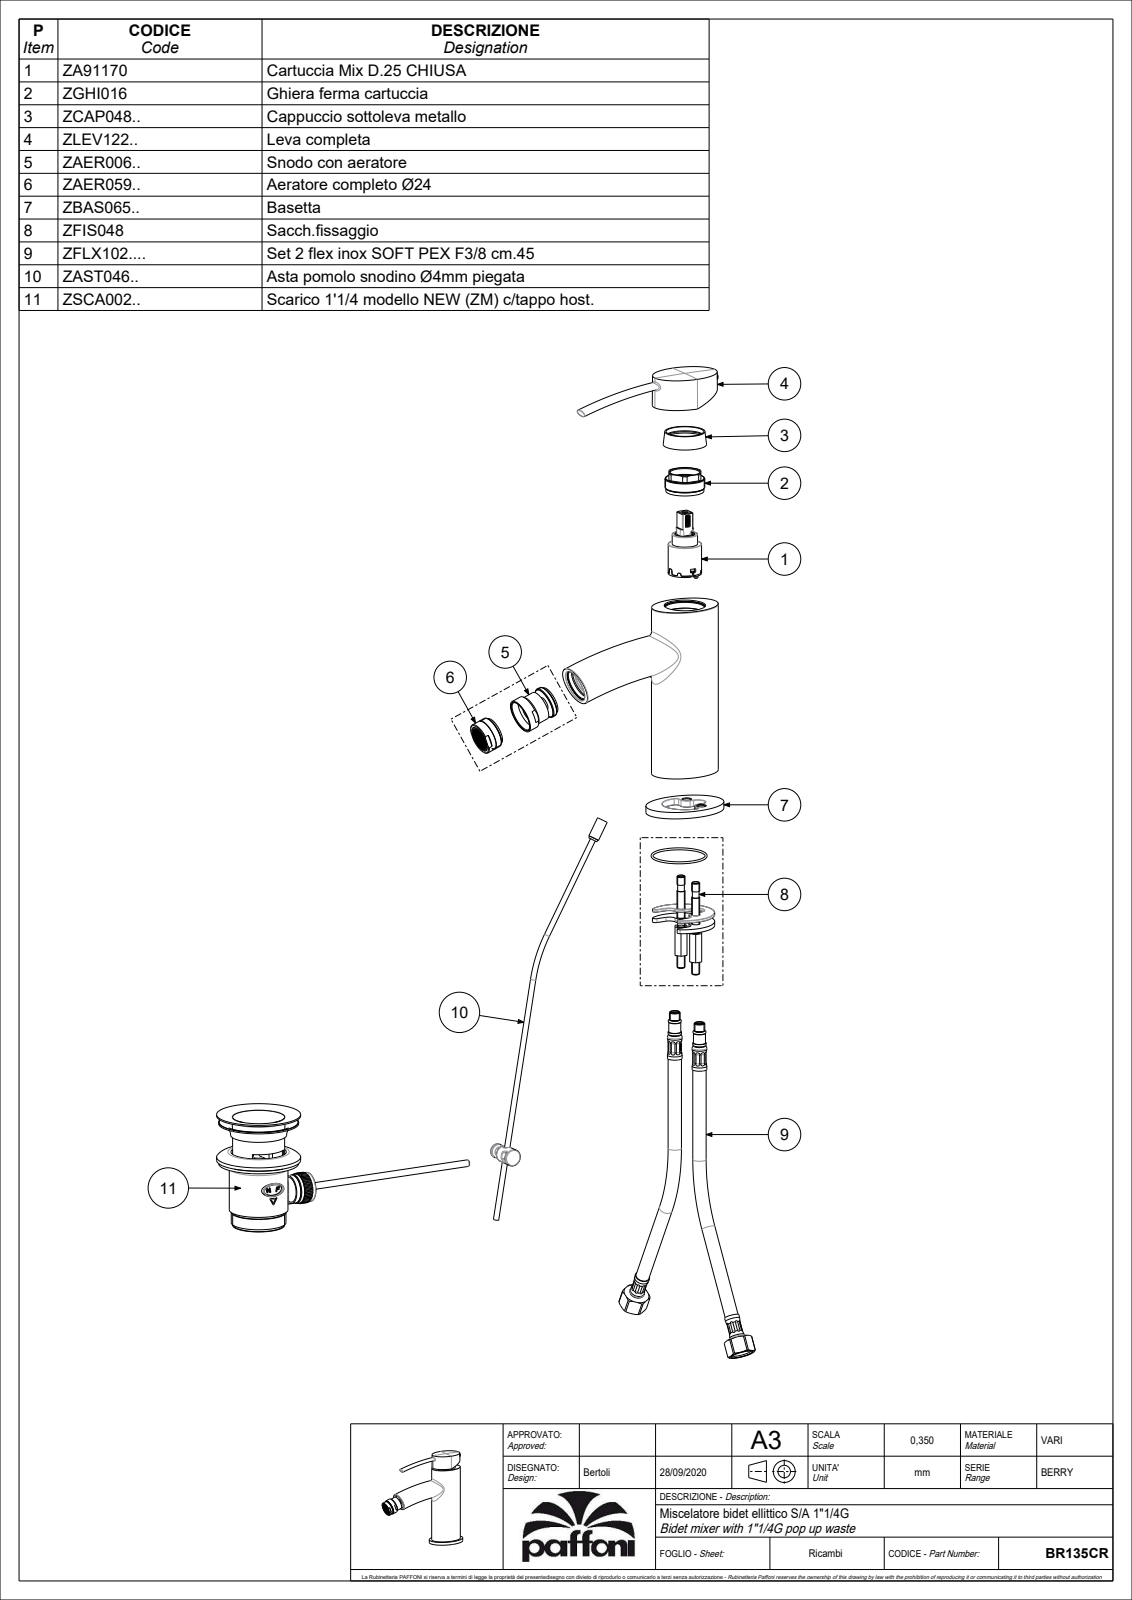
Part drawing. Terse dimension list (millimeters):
name: BR135CR
written by: CREO PARAMETRIC BY PTC INC, 2020044 (CONFIG_CONTROL_DESIGN)
unit: mm
bodies: 7 solids, 2791 faces (1989 planar, 423 cylindrical, 379 other)
size: 170.07 × 159.2 × 46
volume: 165 111 mm³; area: 99 702 mm²
holes: 3× ⌀4.5, 3× ⌀5, 3× ⌀7, 2× ⌀3, 2× ⌀5.5, 2× ⌀6.2, 2× ⌀6.5, 2× ⌀9.4, 2× ⌀16, 2× ⌀20, 1× ⌀5.3, 1× ⌀8
bosses: 3× ⌀10, 3× ⌀5, 2× ⌀11, 2× ⌀9, 2× ⌀6, 2× ⌀4, 1× ⌀38.8, 1× ⌀28.7
rounds: 40× R0.5, 29× R3, 23× R0.3, 18× R1, 13× R0.2, 10× R0.15, 10× R2, 8× R1.5
face distances: 5, 90.5, 156.9, 102.5, 12, 22.9, 151.9, 1.5, 7, 6
hole spacings: 7.5, 11, 11.24, 11.4, 13.46, 13.6, 13.87, 21.1
